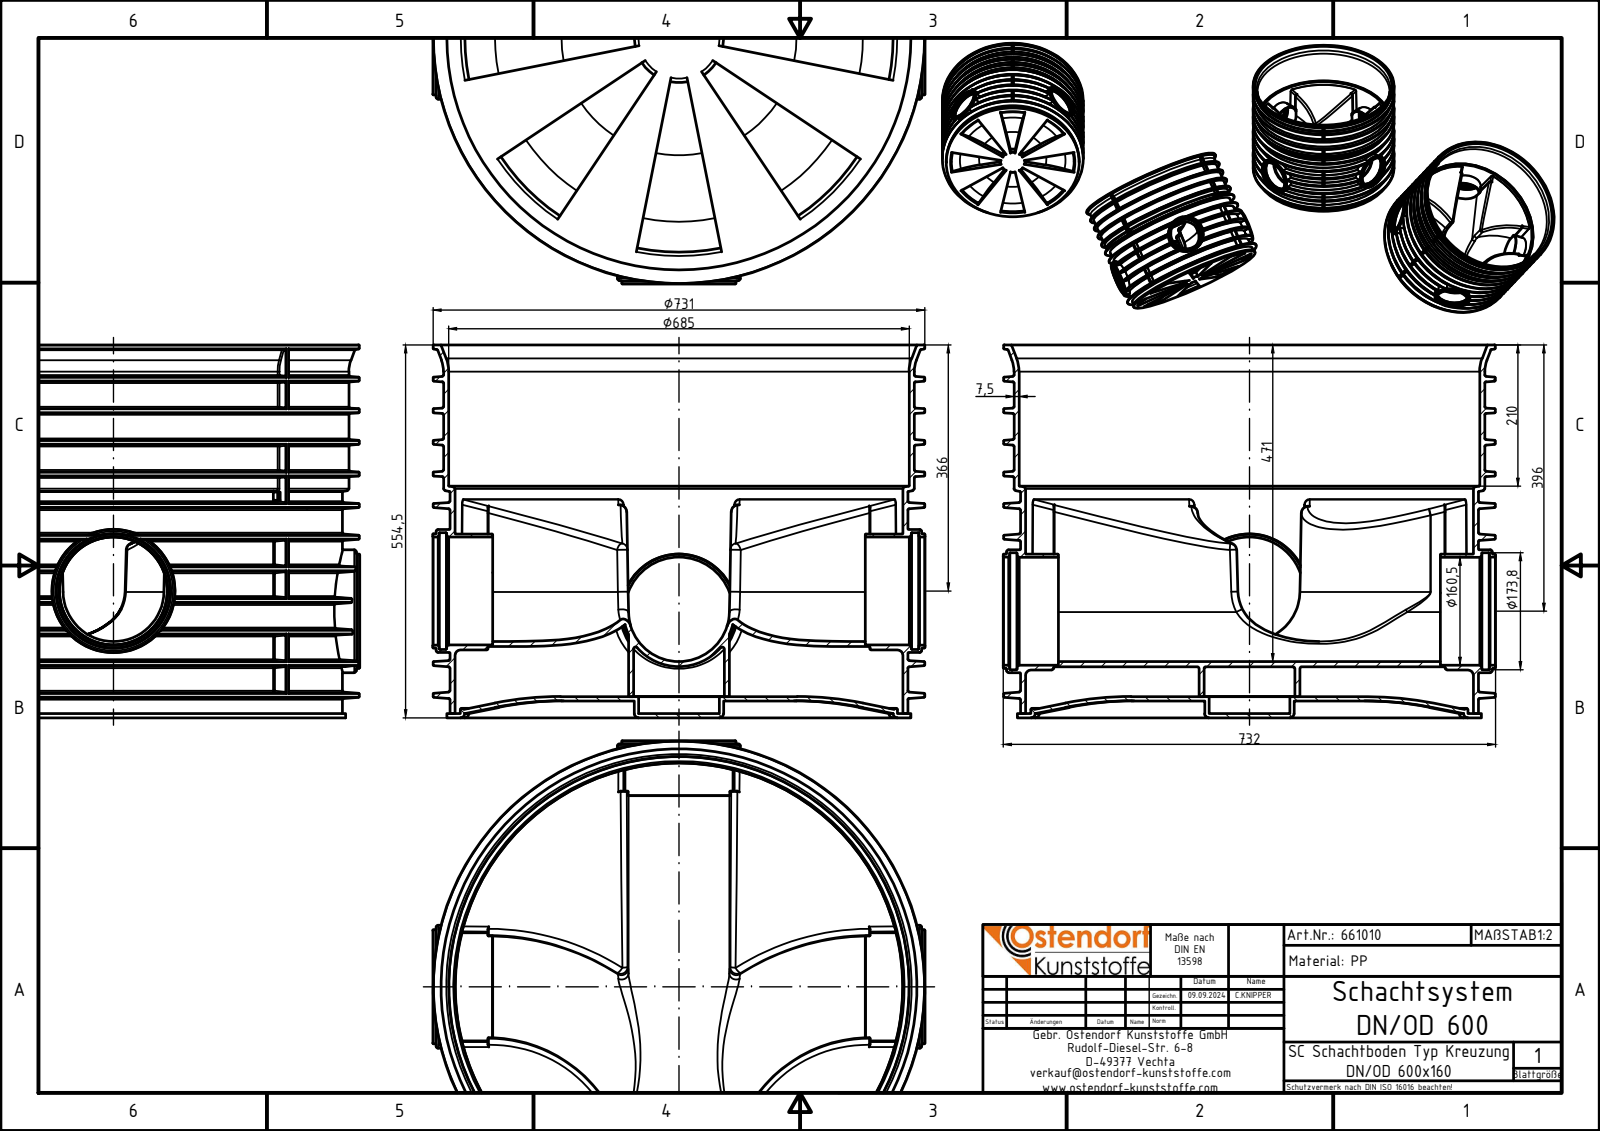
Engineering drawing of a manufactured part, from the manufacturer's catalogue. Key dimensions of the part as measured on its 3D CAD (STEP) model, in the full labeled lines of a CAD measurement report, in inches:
Part name (STEP PRODUCT): 661010z; 661010 Schachtboden DN600 Grundkörper; 661010 Schacht DN600 Boden
STEP written by: Autodesk Inventor 2024 (AUTOMOTIVE_DESIGN)
Units: inches
Bodies: 2 solids, 2157 faces (194 planar, 368 cylindrical, 1595 other)
Overall size (bounding box): 28.819 × 28.819 × 21.831
Volume: 1 438 in³ · Surface area: 8 711 in²
Round holes (diameter × count): ⌀6.319 ×2, ⌀6.327 ×2, ⌀6.331 ×2, ⌀6.685 ×2, ⌀6.843 ×2, ⌀4.724 ×1, ⌀5.315 ×1, ⌀25.197 ×1, ⌀26.22 ×1, ⌀26.969 ×1
Round bosses / shafts (diameter × count): ⌀7.197 ×2, ⌀28.78 ×1, ⌀27.559 ×1, ⌀27.165 ×1, ⌀26.811 ×1, ⌀25.591 ×1, ⌀6.673 ×1, ⌀5.906 ×1
Partial cylindrical surfaces — rounded edges, fillets, slot ends (radius × count): R0.079 ×16, R0.039 ×12, R0.059 ×12, R0.118 ×4, R3.445 ×2, R2.618 ×1, R2.953 ×1, R3.245 ×1
Main face-to-face distances: 0.256, 0.984, 1.24, 0.728, 0.292, 0.298, 0.295, 21.831, 21.575, 20.846
